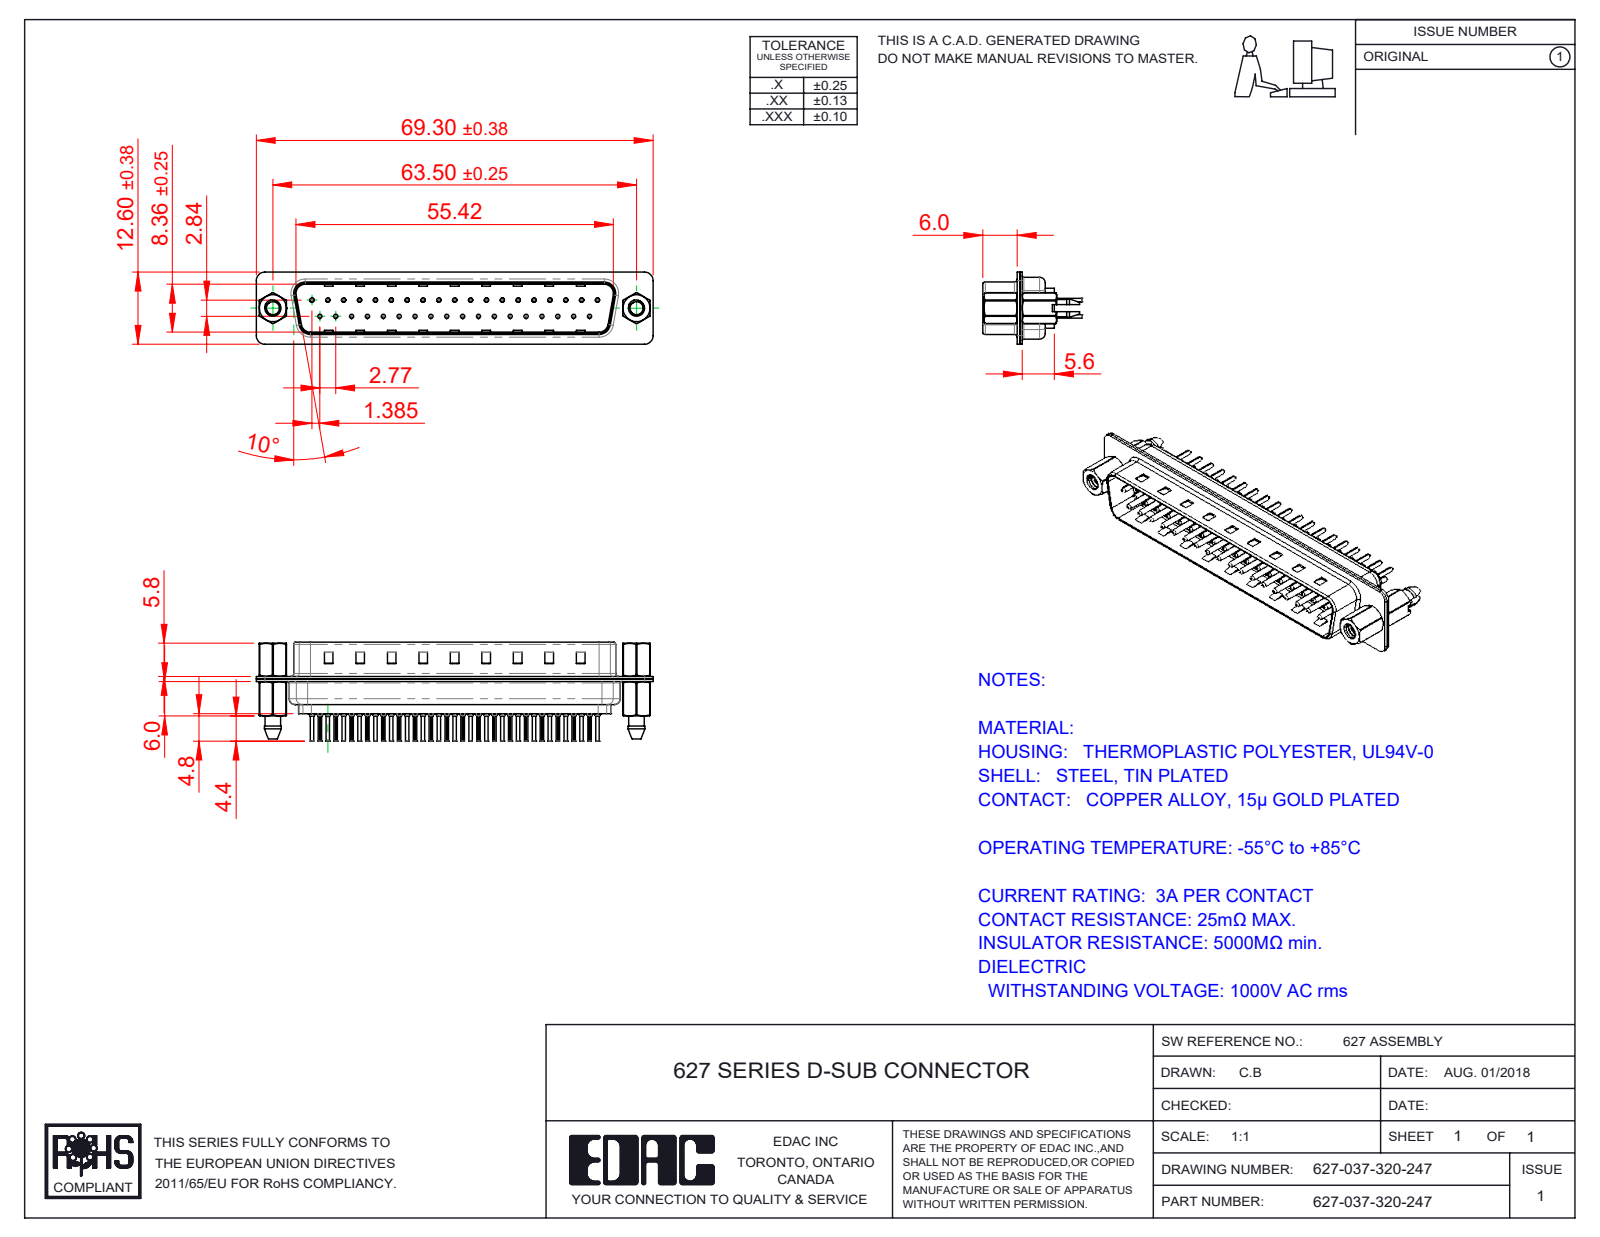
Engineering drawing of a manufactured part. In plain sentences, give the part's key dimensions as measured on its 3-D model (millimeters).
The part is named "627-037-320-047; 627 Housing_37 LP; 627 4-40 Hex Standoff; 627 Shell Rear_37 Contacts (+4 more)". Its 3-D file was written by "SolidWorks 2020 (CONFIG_CONTROL_DESIGN)". It is 44 solids with 4238 faces: 1145 planar, 1614 cylindrical and 1479 other. Overall it measures 69.3 by 17.3 by 12.6 millimeters. Its volume is 4 028 cubic millimeters and its surface area 11 455 square millimeters. Round holes: 37 of diameter 0.2, 37 of diameter 0.35, 37 of diameter 1.1, 37 of diameter 1.6, 2 of diameter 2.26, 2 of diameter 2.29, 2 of diameter 4, 2 of diameter 4.8. Round bosses or shafts: 37 of diameter 2, 37 of diameter 1.5, 37 of diameter 0.75, 37 of diameter 0.6, 2 of diameter 4.9, 2 of diameter 2.79. Partial cylindrical surfaces (rounded edges, fillets, slot ends): 74 of radius 0.1, 18 of radius 1.5, 12 of radius 2, 10 of radius 1.6, 8 of radius 0.5, 4 of radius 0.25, 4 of radius 0.6, 4 of radius 0.65. The main face-to-face distances are 0.4, 0.82, 9.58, 0.45, 8.76, 1.5, 0.9, 1.4, 6.5, 6.05. The hole center spacings are 3.16, 2.77, 5.54, 8.31, 5.04, 10.1, 11.08, 12.78.
